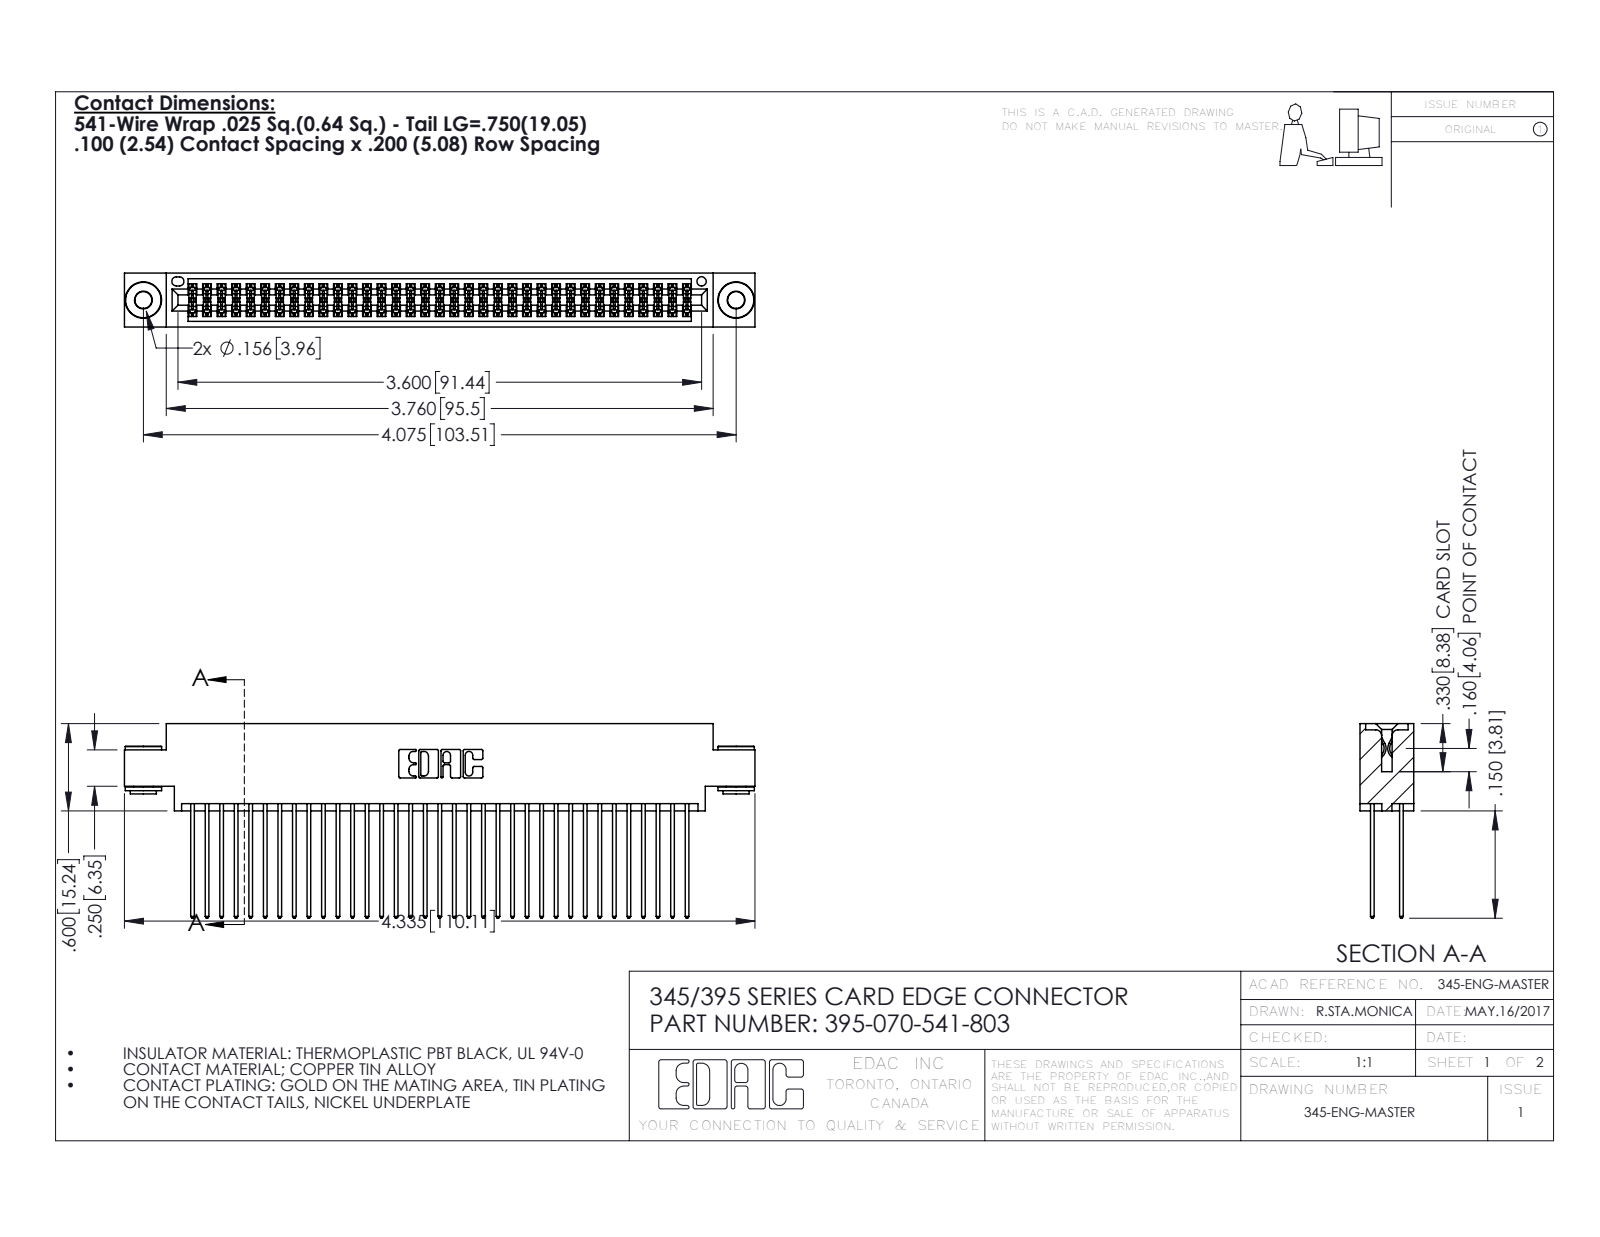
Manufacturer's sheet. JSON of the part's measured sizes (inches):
{"part_name": "345 Part_0.170 Offset - 0.156 Dia-TH; 345-250-002_345-250-002-102; 395-070-541-803; 345-292-001_345-293-141", "step_written_by": "SolidWorks 2016 (CONFIG_CONTROL_DESIGN)", "units": "inches", "bodies": {"solids": 73, "faces": 3668, "planar": 2404, "cylindrical": 1256, "other": 8}, "overall_size": [4.335, 1.337, 0.37], "volume_in3": 0.668, "surface_area_in2": 28.32, "round_holes": [[0.116, 2], [0.156, 2], [0.064, 1]], "round_bosses_or_shafts": [[0.25, 2], [0.18, 2], [0.136, 2]], "partial_cylinders_radius": [[0.006, 105], [0.01, 70], [0.01, 22], [0.007, 6], [0.031, 6], [0.026, 3], [0.014, 2], [0.019, 2]], "face_to_face_distances": [0.072, 0.298, 0.2, 0.098, 0.272, 0.025, 0.37, 0.225, 0.175, 0.149], "hole_center_spacings": [0.27, 3.839, 4.075]}
